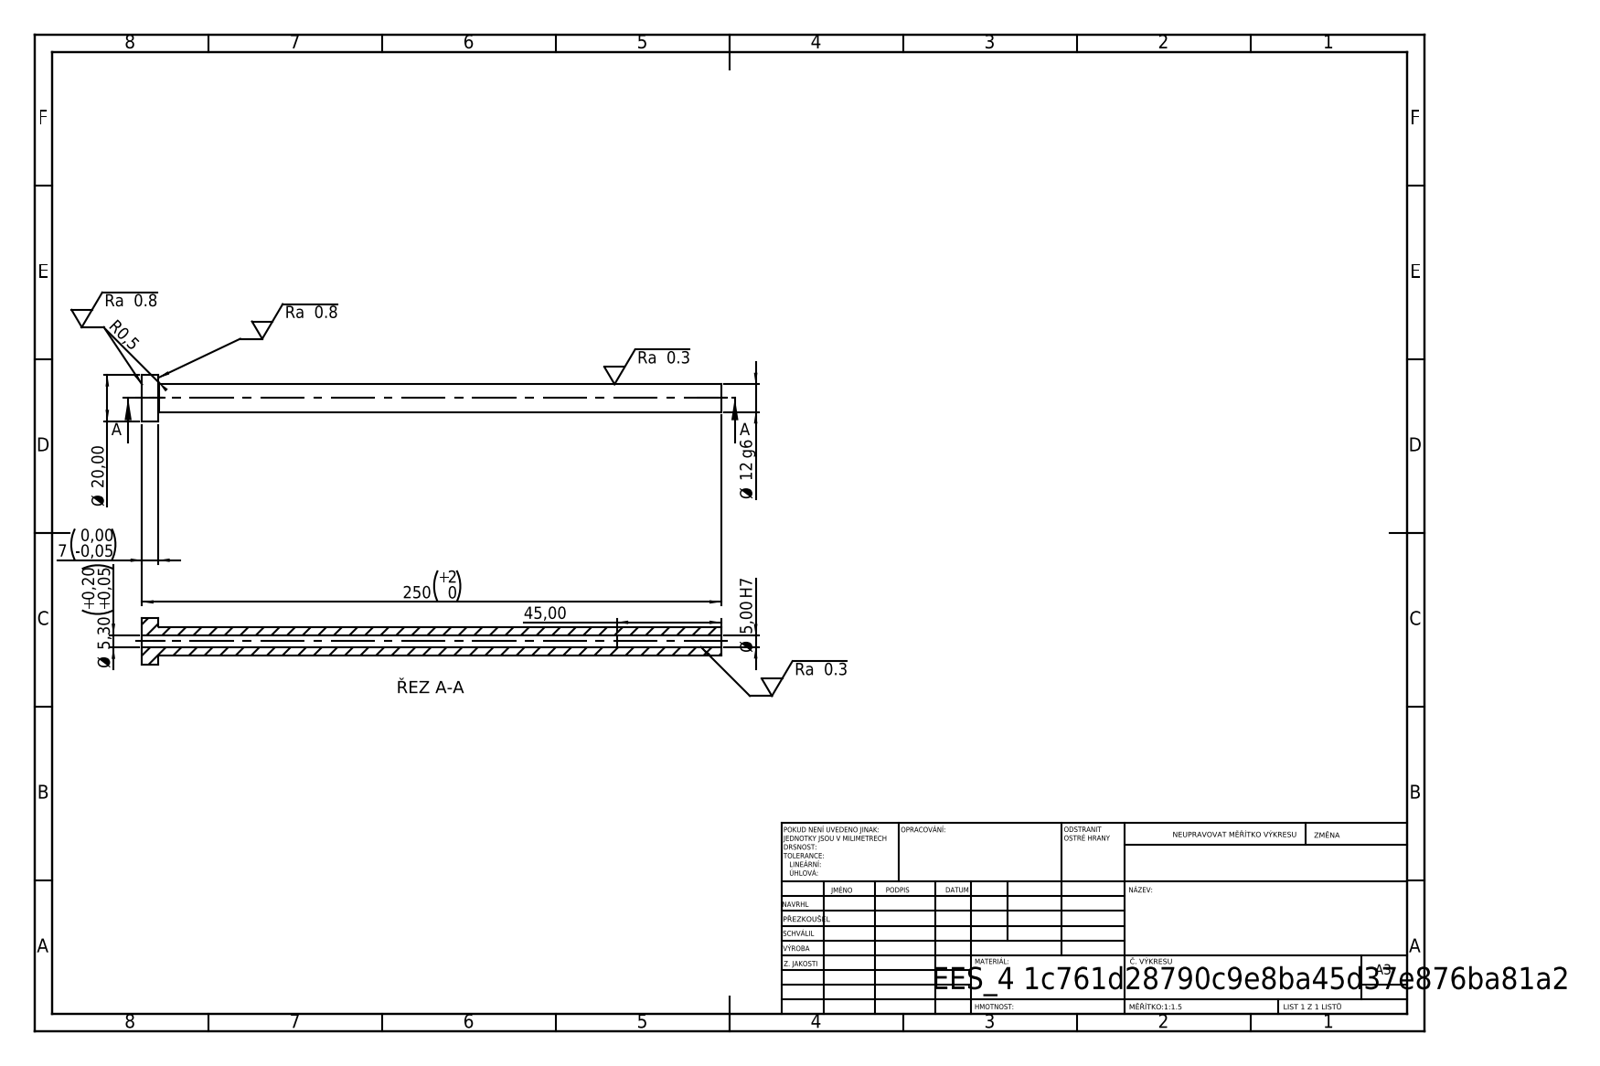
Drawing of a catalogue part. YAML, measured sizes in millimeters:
step_written_by: "SolidWorks 2019 (CONFIG_CONTROL_DESIGN)"
units: millimeters
bodies: {solids: 1, faces: 14, planar: 4, cylindrical: 8, other: 2}
overall_size: [250, 20, 20]
volume: 24278
surface_area: 14302
round_holes:
  - {diameter: 5, count: 1}
  - {diameter: 5.3, count: 1}
round_bosses_or_shafts:
  - {diameter: 20, count: 1}
  - {diameter: 12, count: 1}
face_to_face_distances: [7, 250, 243, 205, 198, 45]
